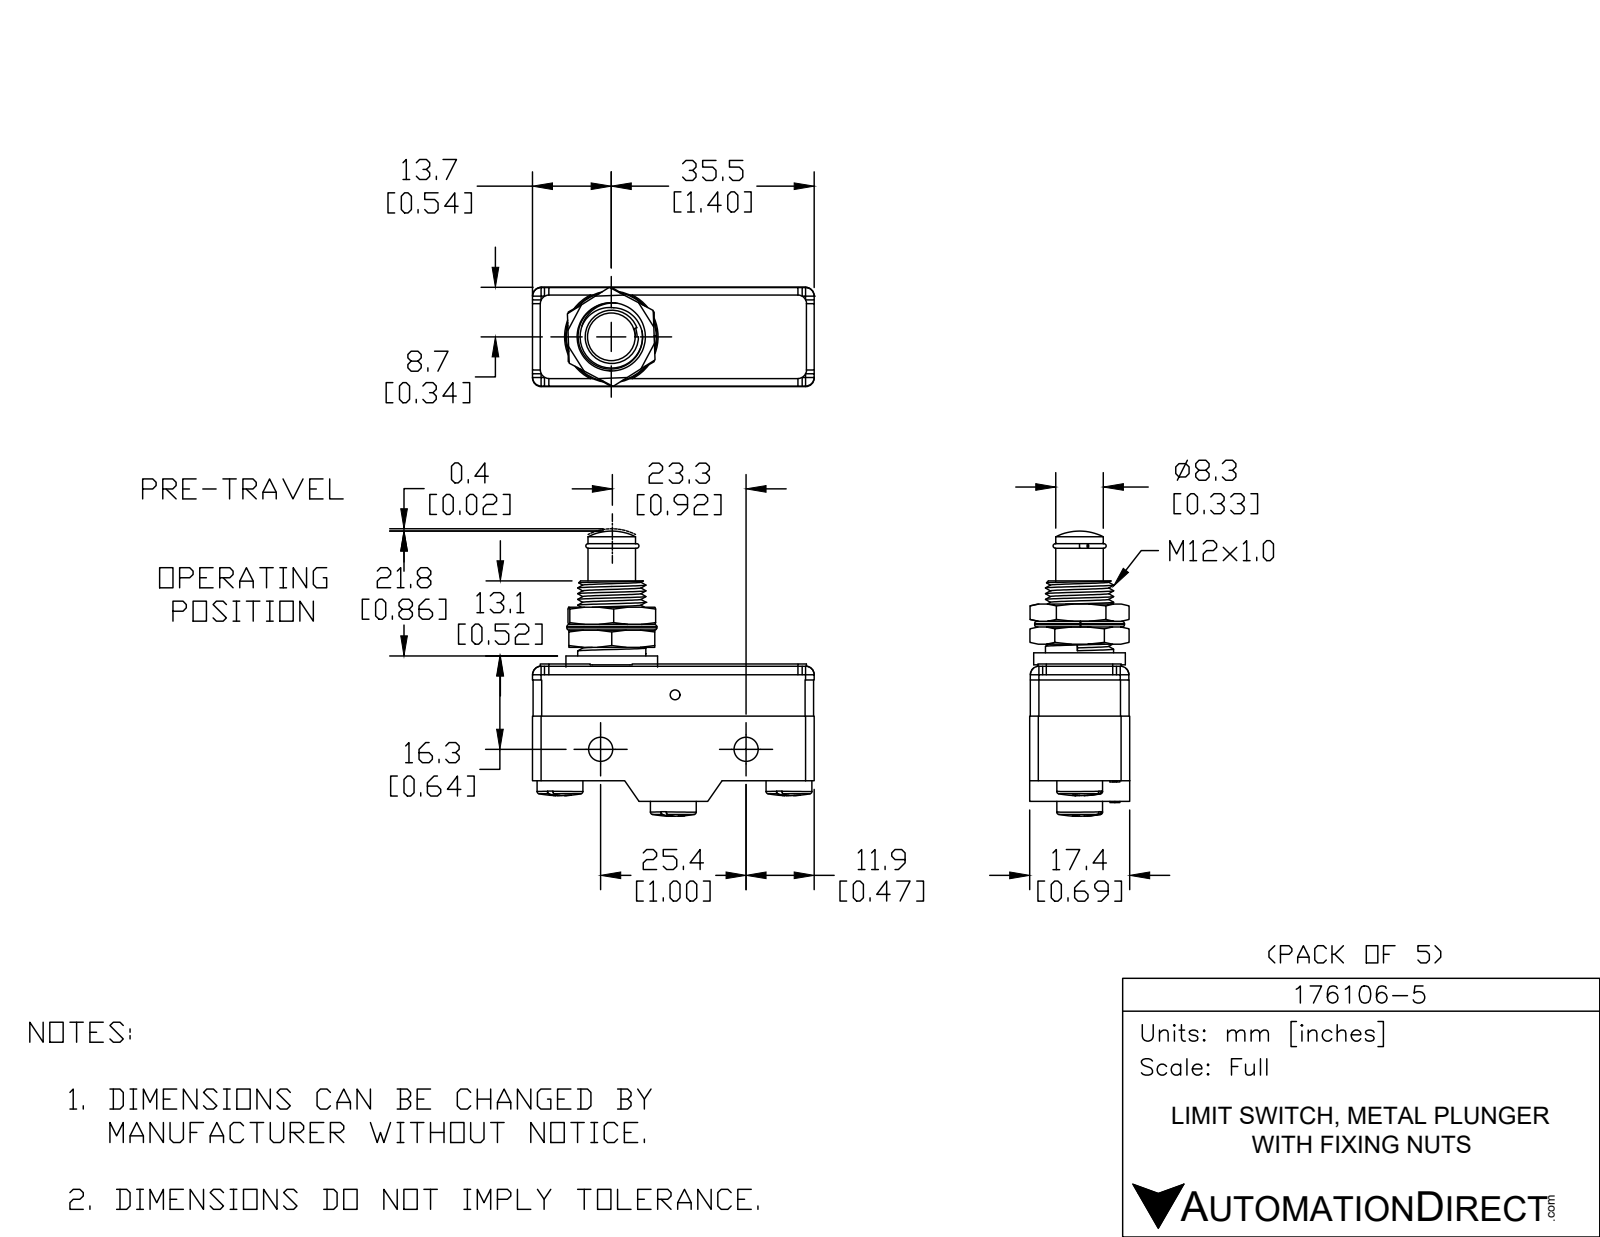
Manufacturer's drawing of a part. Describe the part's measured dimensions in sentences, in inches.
The part is named "176-MS (Screw Terminal)-Panel Mount Plunger". Its 3-D file was written by "SolidWorks 2018 (AUTOMOTIVE_DESIGN)". It is 7 solids with 554 faces: 273 planar, 106 cylindrical and 175 other. Overall it measures 1.937 by 1.921 by 0.687 inches. Its volume is 1.165 cubic inches and its surface area 14.55 square inches. Round holes: 3 of diameter 0.236, 2 of diameter 0.165, 1 of diameter 0.067, 1 of diameter 0.331, 1 of diameter 0.439, 1 of diameter 0.491. Round bosses or shafts: 3 of diameter 0.315, 3 of diameter 0.15, 1 of diameter 0.63, 1 of diameter 0.618, 1 of diameter 0.469, 1 of diameter 0.327, 1 of diameter 0.295. Partial cylindrical surfaces (rounded edges, fillets, slot ends): 24 of radius 0.059, 12 of radius 0.012, 3 of radius 0.116, 1 of radius 0.321. The main face-to-face distances are 0.683, 0.687, 0.803, 0.797, 0.68, 0.142, 0.939, 1.933, 1.937, 0.945. The hole center spacings are 0.352, 0.427, 0.615, 0.634, 0.78, 0.795, 1, 1.222.
